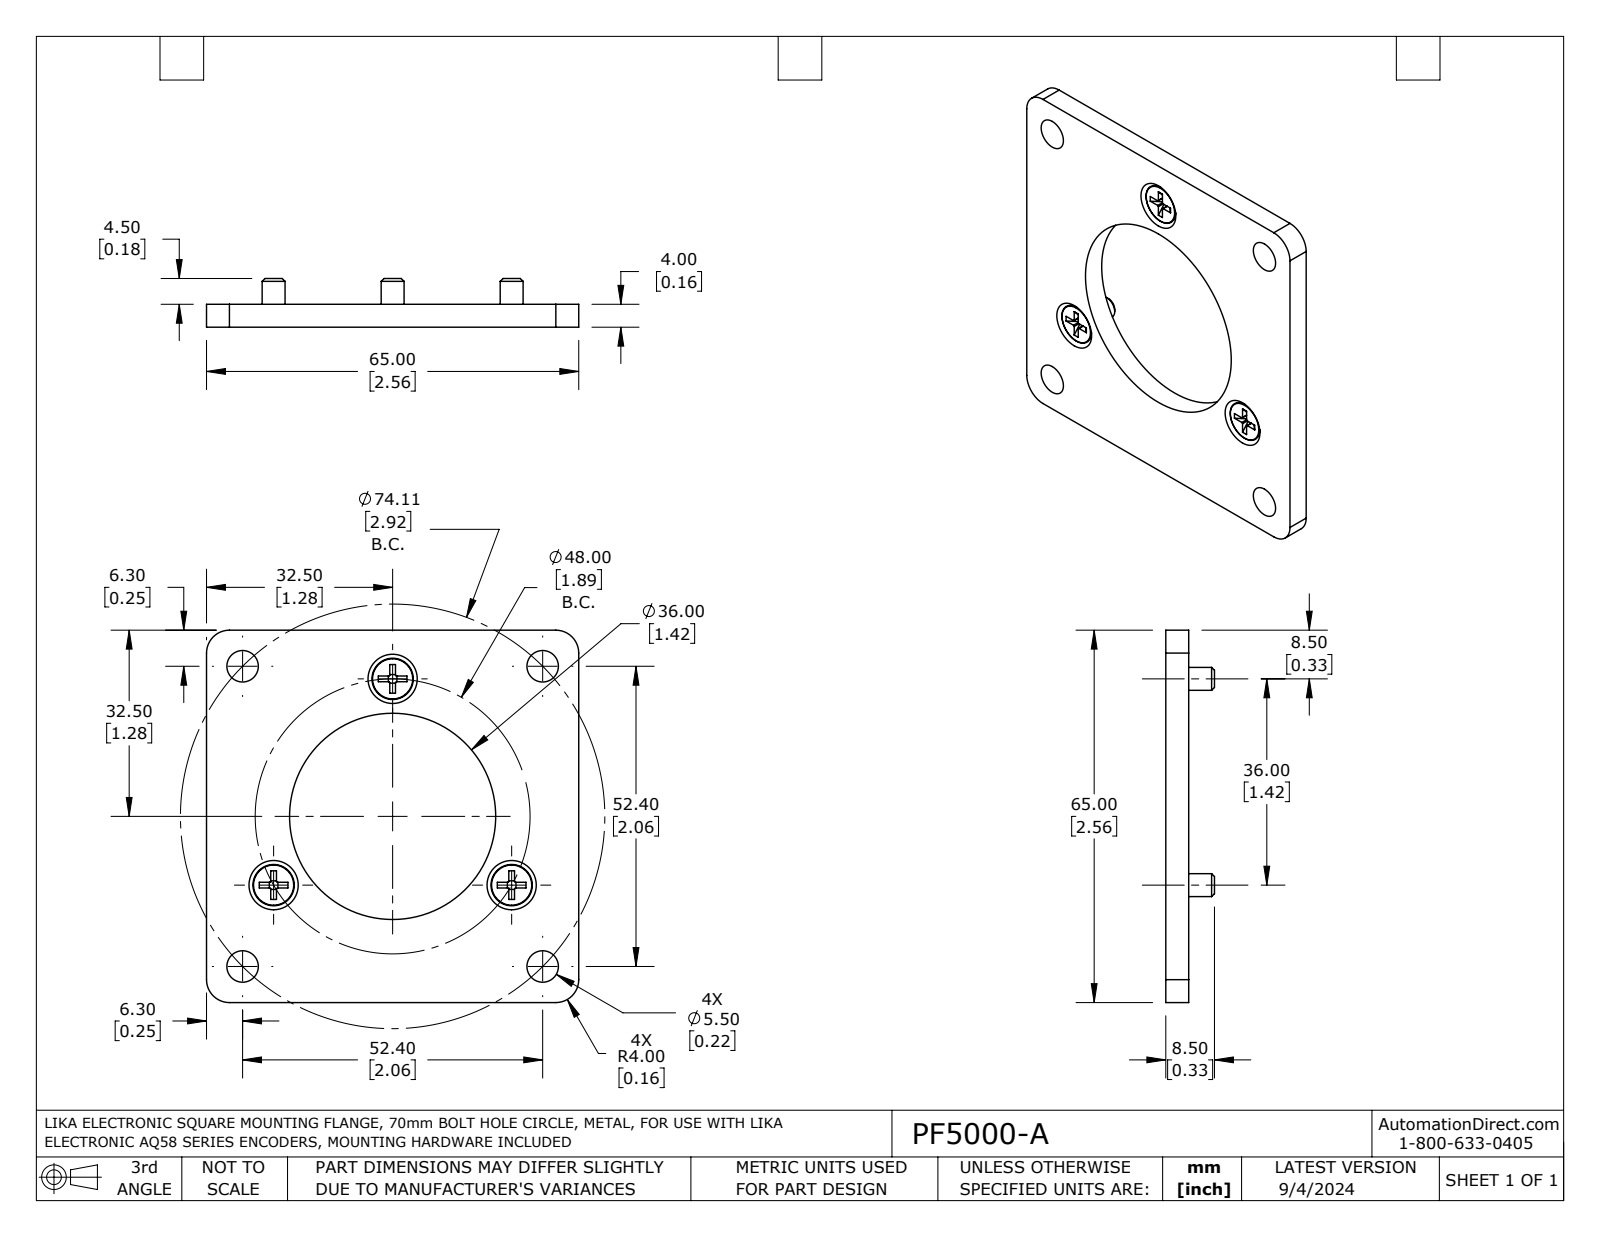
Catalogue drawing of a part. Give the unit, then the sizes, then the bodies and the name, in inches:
Units: inches
Overall size (bounding box): 2.559 × 2.559 × 0.335
Round holes (diameter × count): ⌀0.217 ×4, ⌀0.169 ×3, ⌀1.417 ×1
Round bosses / shafts (diameter × count): ⌀0.157 ×3
Partial cylindrical surfaces — rounded edges, fillets, slot ends (radius × count): R0.007 ×9, R0.157 ×4, R0.008 ×3
Main face-to-face distances: 0.157, 2.559, 0.02, 0.138, 0.315, 0.335, 0.177, 0.039, 0.818, 0.078
Hole centre spacings: 1.459, 2.063, 0.945, 0.598, 1.035, 1.519, 1.637, 1.932
Volume: 0.759 in³ · Surface area: 13.23 in²
Bodies: 4 solids, 119 faces (51 planar, 38 cylindrical, 30 other)
Part name (STEP PRODUCT): PF5000-A
STEP written by: SolidWorks 2021 (AUTOMOTIVE_DESIGN)
